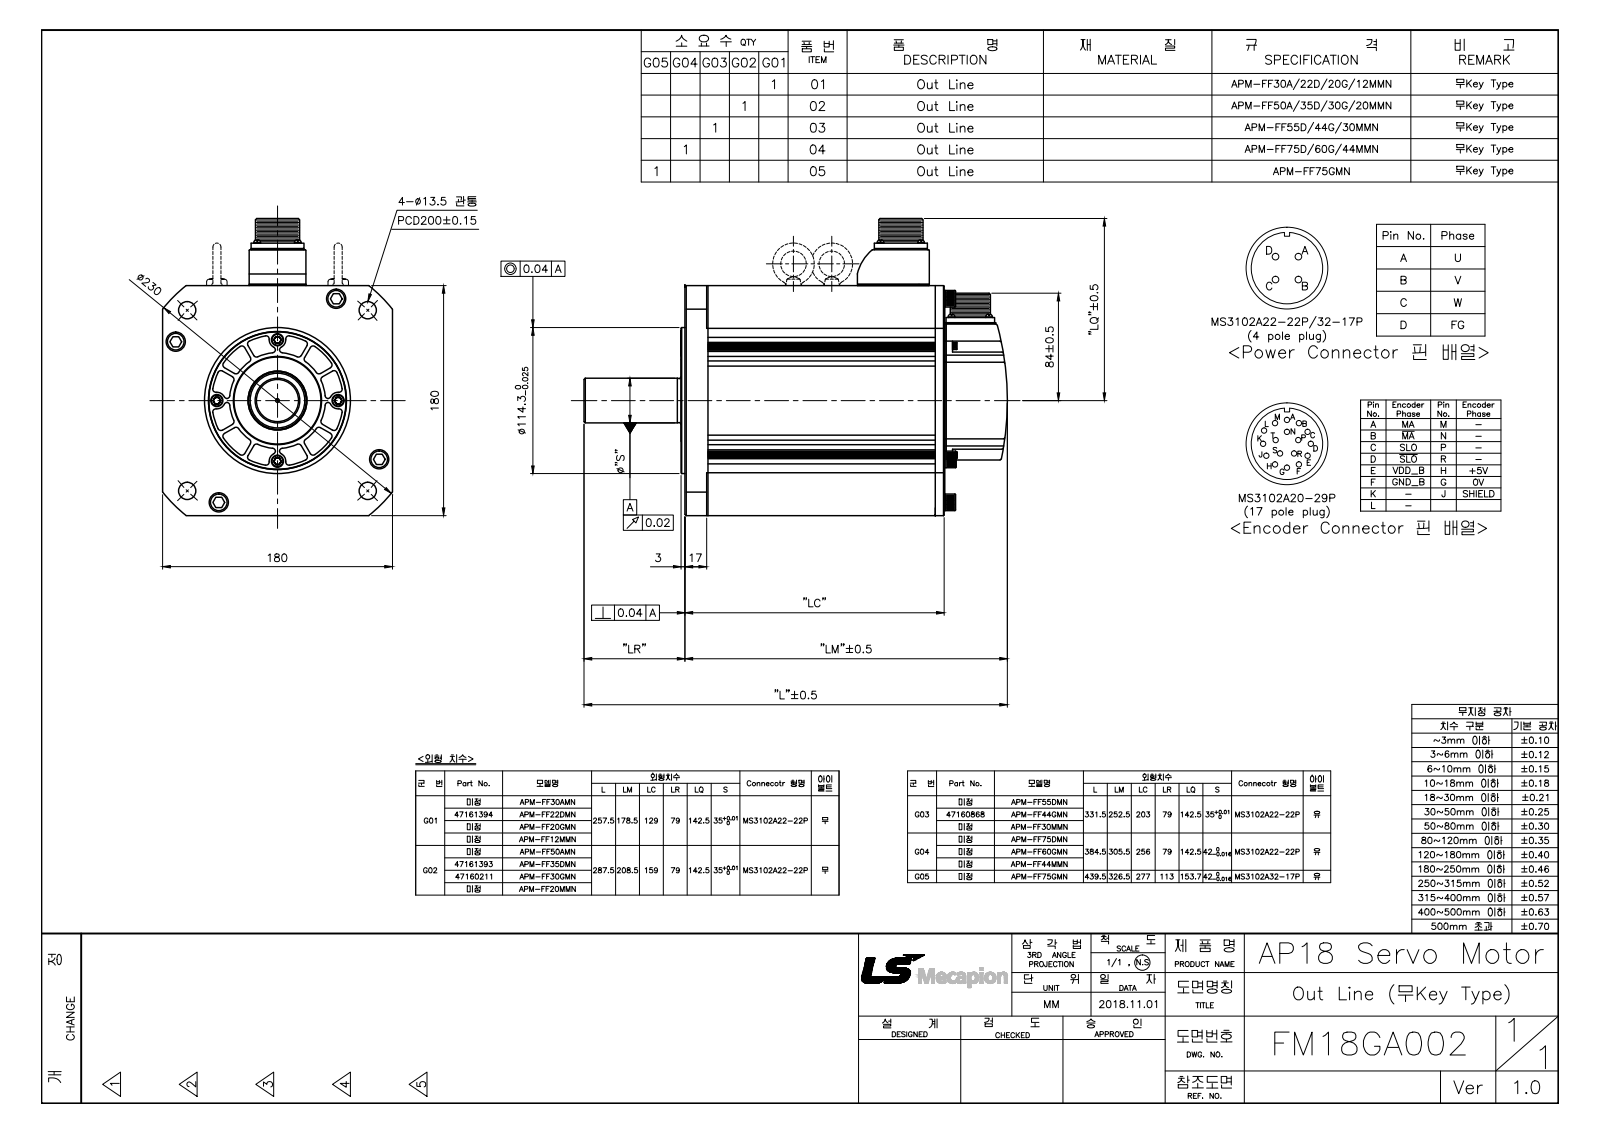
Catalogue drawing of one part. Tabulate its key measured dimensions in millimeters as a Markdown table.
| quantity | value |
| --- | --- |
| part name | FM18GA002G03_Out Line(APM-FF55D_N,FF44G_N,FF30M_N) |
| STEP written by | SolidWorks 2011 (AUTOMOTIVE_DESIGN) |
| units | millimeters |
| bodies | 56 solids, 2357 faces (790 planar, 878 cylindrical, 689 other) |
| overall size | 331.5 × 232.5 × 180 |
| volume | 6 231 000 mm³ |
| surface area | 512 329 mm² |
| round holes (diameter × count) | 3 × 13, 2.5 × 9, 3.05 × 8, 6 × 8, 9.5 × 8, 6.8 × 6, 3.5 × 4, 3.6 × 4, 3.7 × 4, 5 × 4, 9 × 4, 9.2 × 4 |
| round bosses / shafts (diameter × count) | 1.6 × 17, 5.4 × 8, 13.2 × 4, 13 × 4, 8.5 × 4, 8 × 4, 5.5 × 4, 3 × 4 |
| partial cylindrical surfaces (radius × count) | 0.5 × 124, 2.5 × 56, 4 × 24, 2 × 17, 1 × 14, 4.5 × 12, 6.5 × 4, 0.3 × 2 |
| main face-to-face distances | 178, 1, 180, 18, 8, 10, 7.5, 7, 33.5, 146.5 |
| hole center spacings | 32.56, 74.42, 137.74, 1.06, 20.79, 22.49, 23.55, 26.28 |
